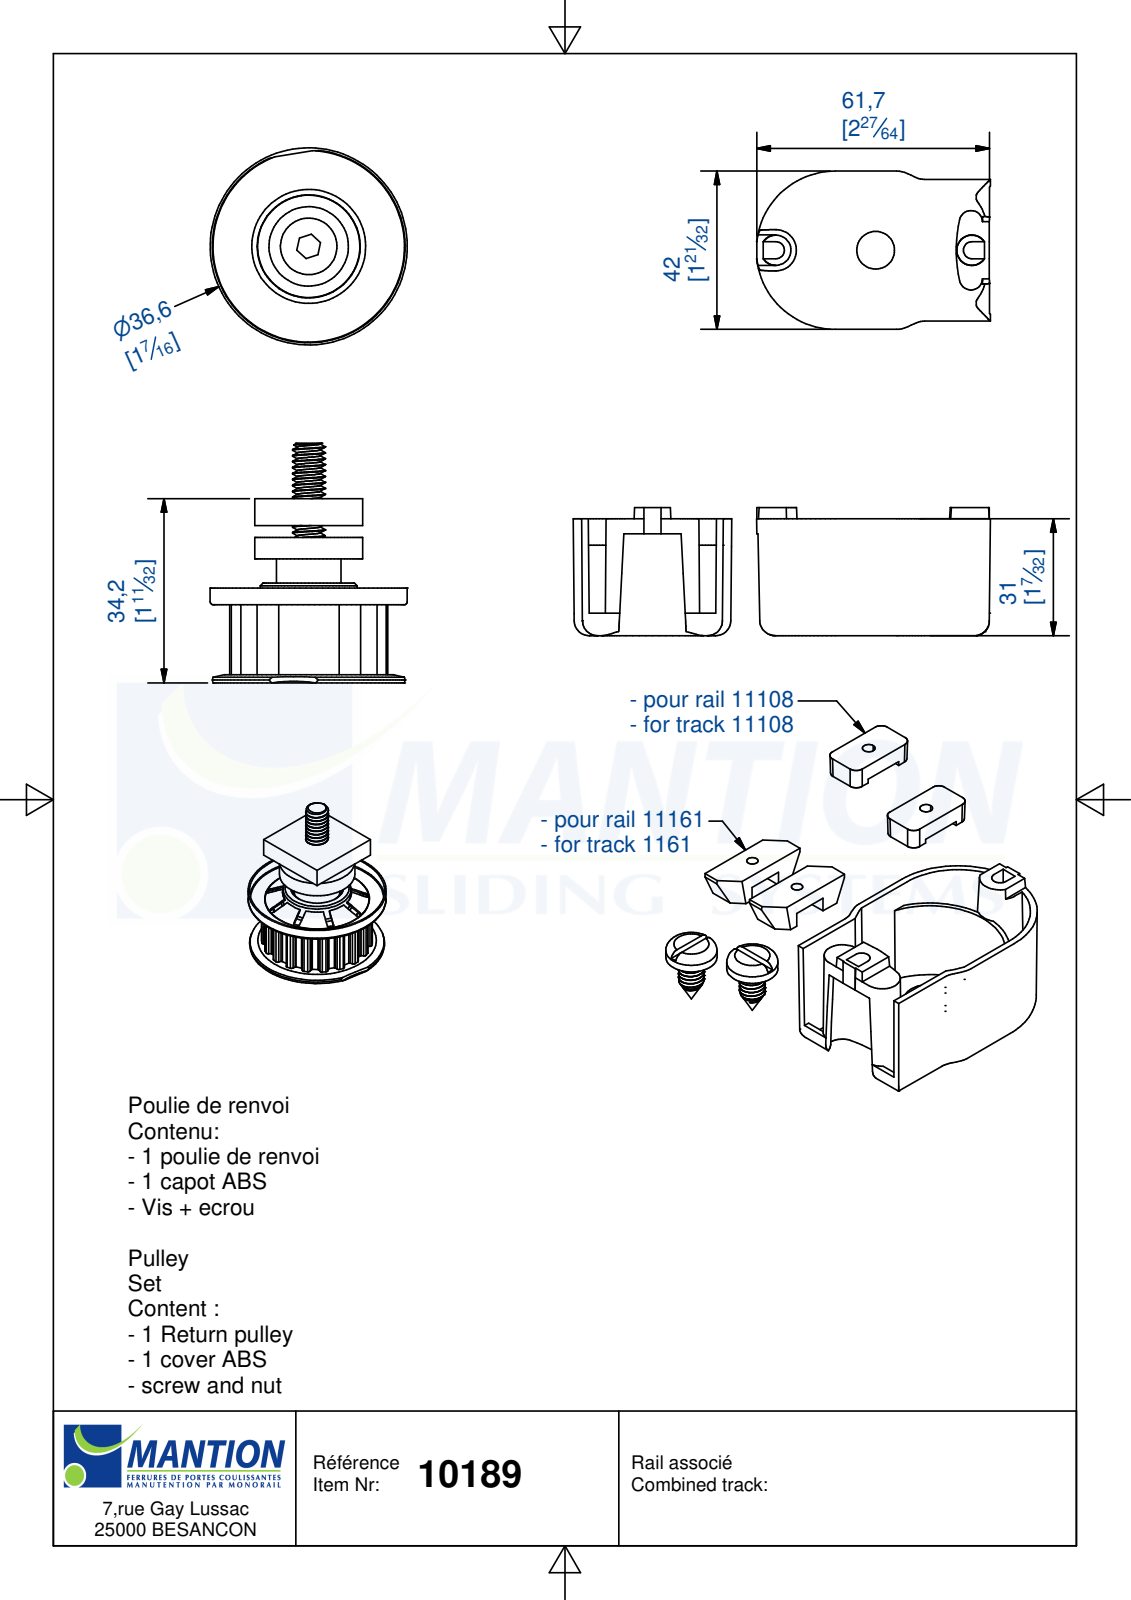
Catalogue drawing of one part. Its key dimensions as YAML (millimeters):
part_name: "10189; 20109-B; 20646; vis tete ronde M6x40 (+4 more)"
step_written_by: "Autodesk Inventor 2019 (AUTOMOTIVE_DESIGN)"
units: millimeters
bodies: {solids: 11, faces: 341, planar: 113, cylindrical: 146, other: 82}
overall_size: [44.5, 36.6, 36.6]
volume: 13023
surface_area: 12679
round_holes:
  - {diameter: 4.92, count: 1}
  - {diameter: 6.1, count: 1}
  - {diameter: 13, count: 1}
  - {diameter: 14.76, count: 1}
  - {diameter: 19, count: 1}
  - {diameter: 35.8, count: 1}
round_bosses_or_shafts:
  - {diameter: 36.6, count: 1}
  - {diameter: 20, count: 1}
  - {diameter: 18, count: 1}
  - {diameter: 12, count: 1}
  - {diameter: 10.5, count: 1}
  - {diameter: 10.24, count: 1}
  - {diameter: 6, count: 1}
partial_cylinders:
  - {radius: 0.3, count: 38}
  - {radius: 0.62, count: 38}
  - {radius: 0.85, count: 9}
  - {radius: 14.7, count: 1}
face_to_face_distances: [4, 12.5, 0.4, 14.5, 4.4, 34.2, 29.2, 14.7, 19.7, 5]
